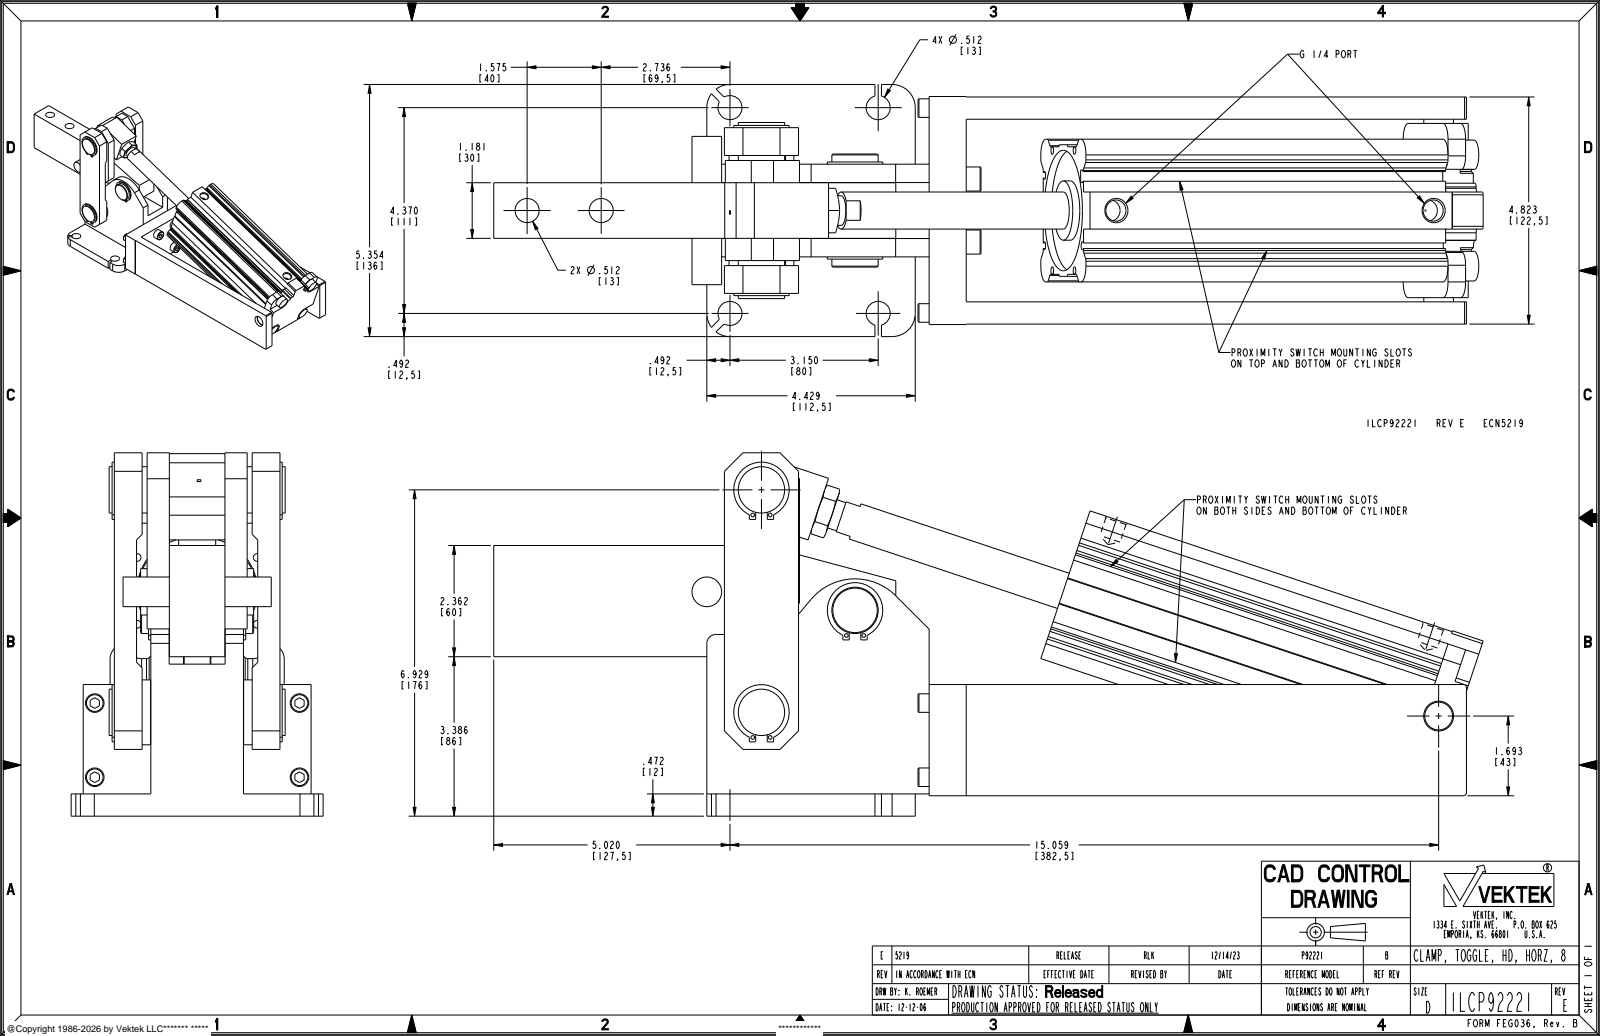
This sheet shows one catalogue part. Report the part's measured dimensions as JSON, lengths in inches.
{"part_name": "ILCP92221", "step_written_by": "CREO PARAMETRIC BY PTC INC, 2021164 (AUTOMOTIVE_DESIGN)", "units": "inches", "bodies": {"solids": 1, "faces": 686, "planar": 415, "cylindrical": 207, "other": 64}, "overall_size": [21.025, 7.717, 5.354], "volume_in3": 161.1, "surface_area_in2": 689.1, "round_holes": [[0.079, 6], [0.512, 6], [0.262, 4], [0.335, 4], [0.451, 2], [0.634, 1], [2.48, 1], [2.559, 1]], "round_bosses_or_shafts": [[0.63, 7], [0.984, 4], [0.512, 4], [0.394, 4], [0.315, 4], [1.177, 3], [1.378, 1], [1.26, 1]], "partial_cylinders_radius": [[0.079, 19], [0.335, 8], [0.087, 7], [0.492, 7], [0.039, 4], [0.394, 4], [0.059, 2], [0.295, 2]], "face_to_face_distances": [0.472, 4.35, 1.575, 0.394, 1.427, 3.396, 0.955, 2.923, 1.348, 1.821], "hole_center_spacings": [0.369, 1.575, 1.339, 2.067, 2.94, 3.15, 3.241, 3.502]}
